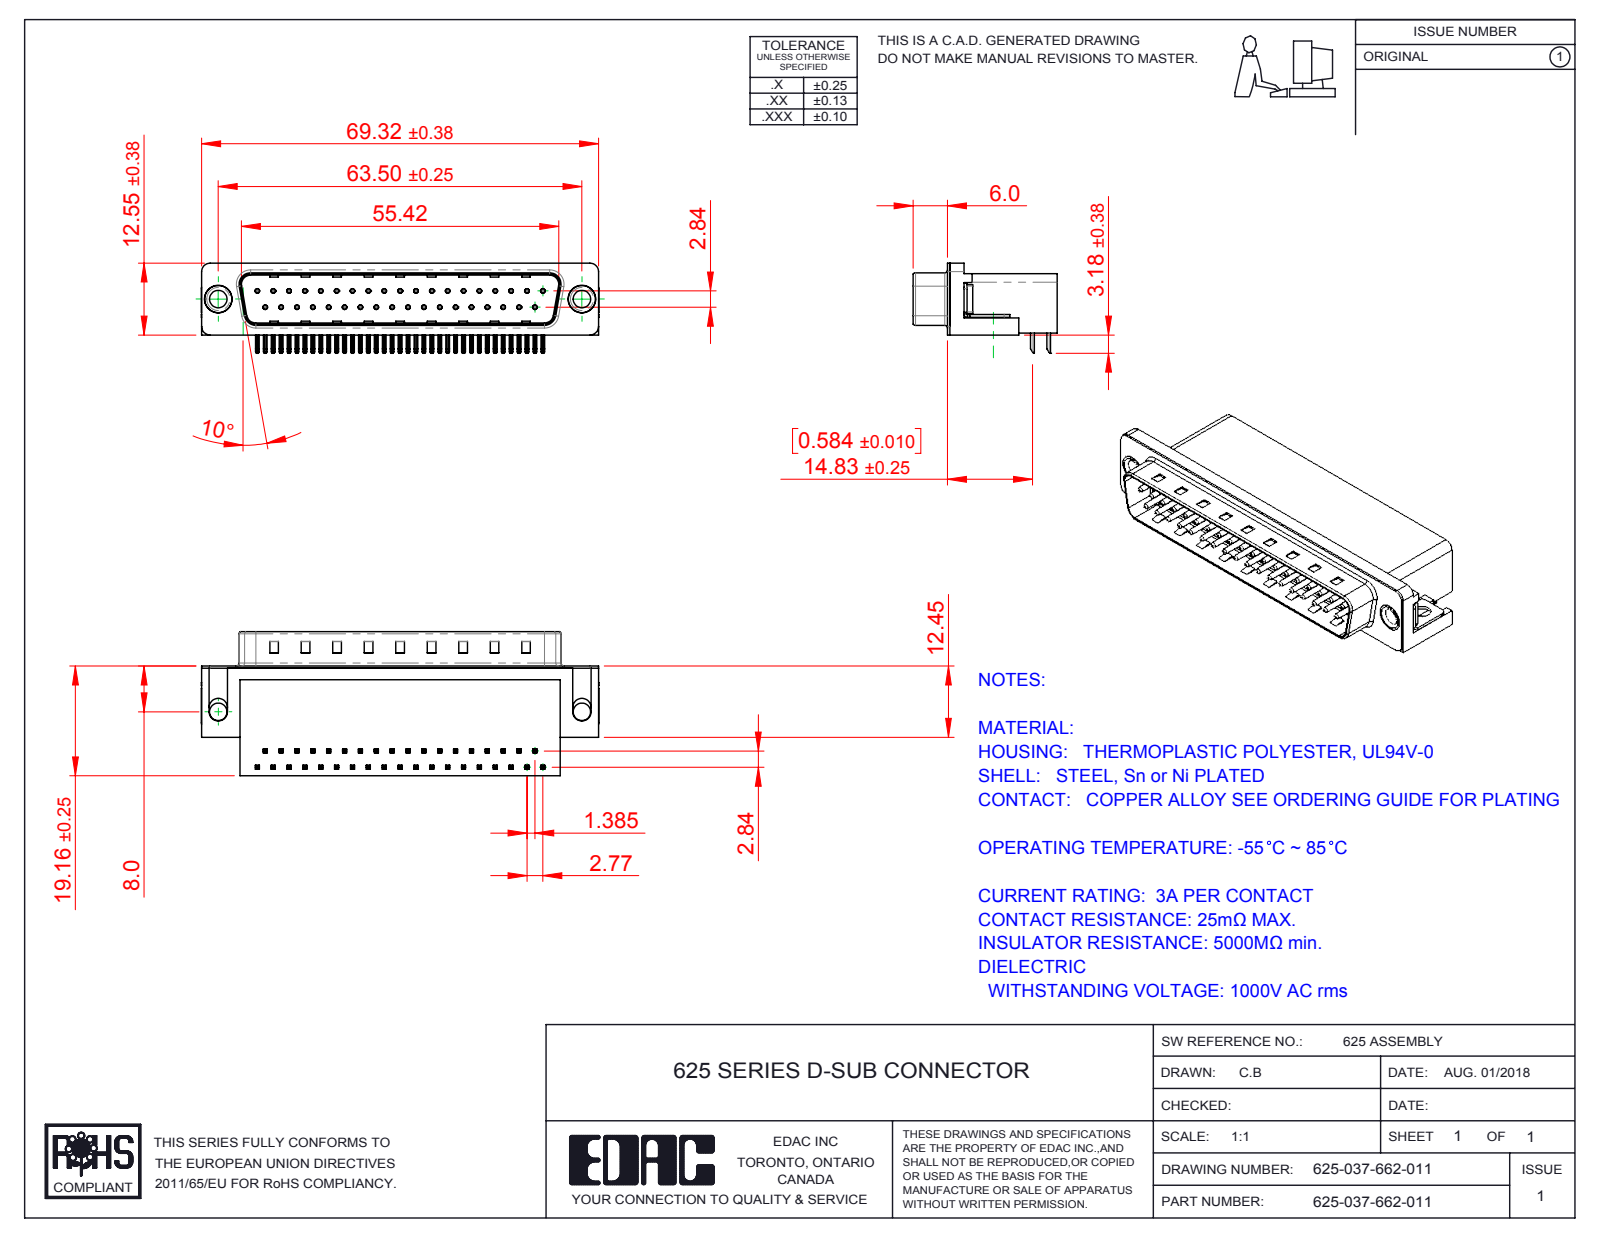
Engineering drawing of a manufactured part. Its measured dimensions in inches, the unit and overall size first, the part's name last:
Units: inches
Overall size (bounding box): 2.732 × 0.991 × 0.619
Round holes (diameter × count): ⌀0.014 ×37, ⌀0.031 ×37, ⌀0.12 ×4, ⌀0.157 ×2, ⌀0.189 ×2, ⌀0.197 ×2
Round bosses / shafts (diameter × count): ⌀0.03 ×37, ⌀0.193 ×2, ⌀0.187 ×2, ⌀0.152 ×2
Partial cylindrical surfaces — rounded edges, fillets, slot ends (radius × count): R0.01 ×156, R0.005 ×74, R0.039 ×16, R0.02 ×9, R0.063 ×8, R0.059 ×7, R0.035 ×4, R0.079 ×4
Main face-to-face distances: 0.407, 0.016, 0.739, 0.345, 0.754, 0.112, 0.082, 0.398, 0.069, 0.329
Hole centre spacings: 0.124, 0.109, 0.218, 0.327, 0.436, 0.545, 0.763, 0.872
Volume: 0.768 in³ · Surface area: 18.16 in²
Bodies: 43 solids, 3161 faces (2013 planar, 899 cylindrical, 249 other)
Part name (STEP PRODUCT): 625 Contact Top; 625-037-662-011; 625 Shell_37 Socket; 625 Thru Hole Rivet (+3 more)
STEP written by: SolidWorks 2016 (CONFIG_CONTROL_DESIGN)
